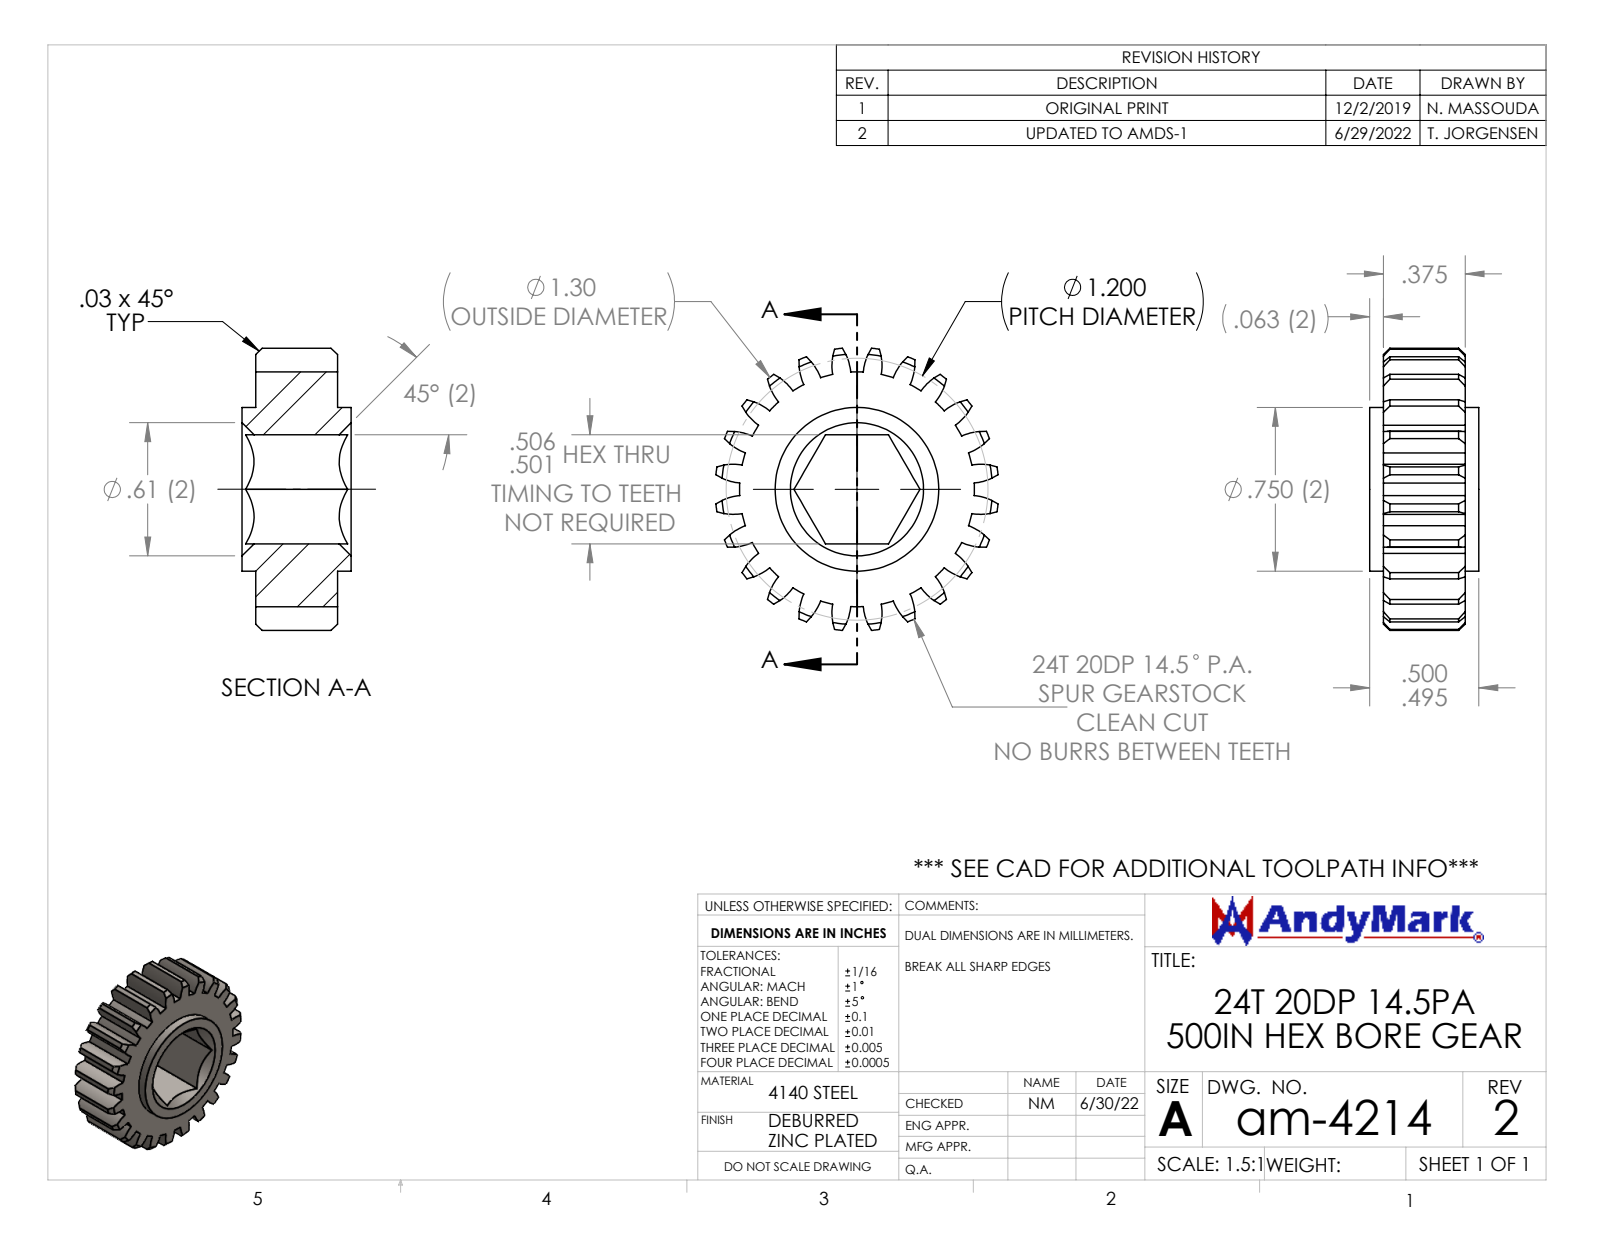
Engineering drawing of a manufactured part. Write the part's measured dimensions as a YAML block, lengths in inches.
part_name: "am-4214 24T 20DP 500hex 375 FW"
step_written_by: "SolidWorks 2022 (CONFIG_CONTROL_DESIGN)"
units: inches
bodies: {solids: 1, faces: 167, planar: 10, cylindrical: 105, other: 52}
overall_size: [1.293, 1.293, 0.5]
volume: 0.353
surface_area: 5.716
round_bosses_or_shafts:
  - {diameter: 0.75, count: 1}
partial_cylinders:
  - {radius: 0.24, count: 48}
  - {radius: 0.538, count: 1}
  - {radius: 0.65, count: 1}
face_to_face_distances: [0.375, 0.5, 0.063, 0.438, 0.437, 0.062]
